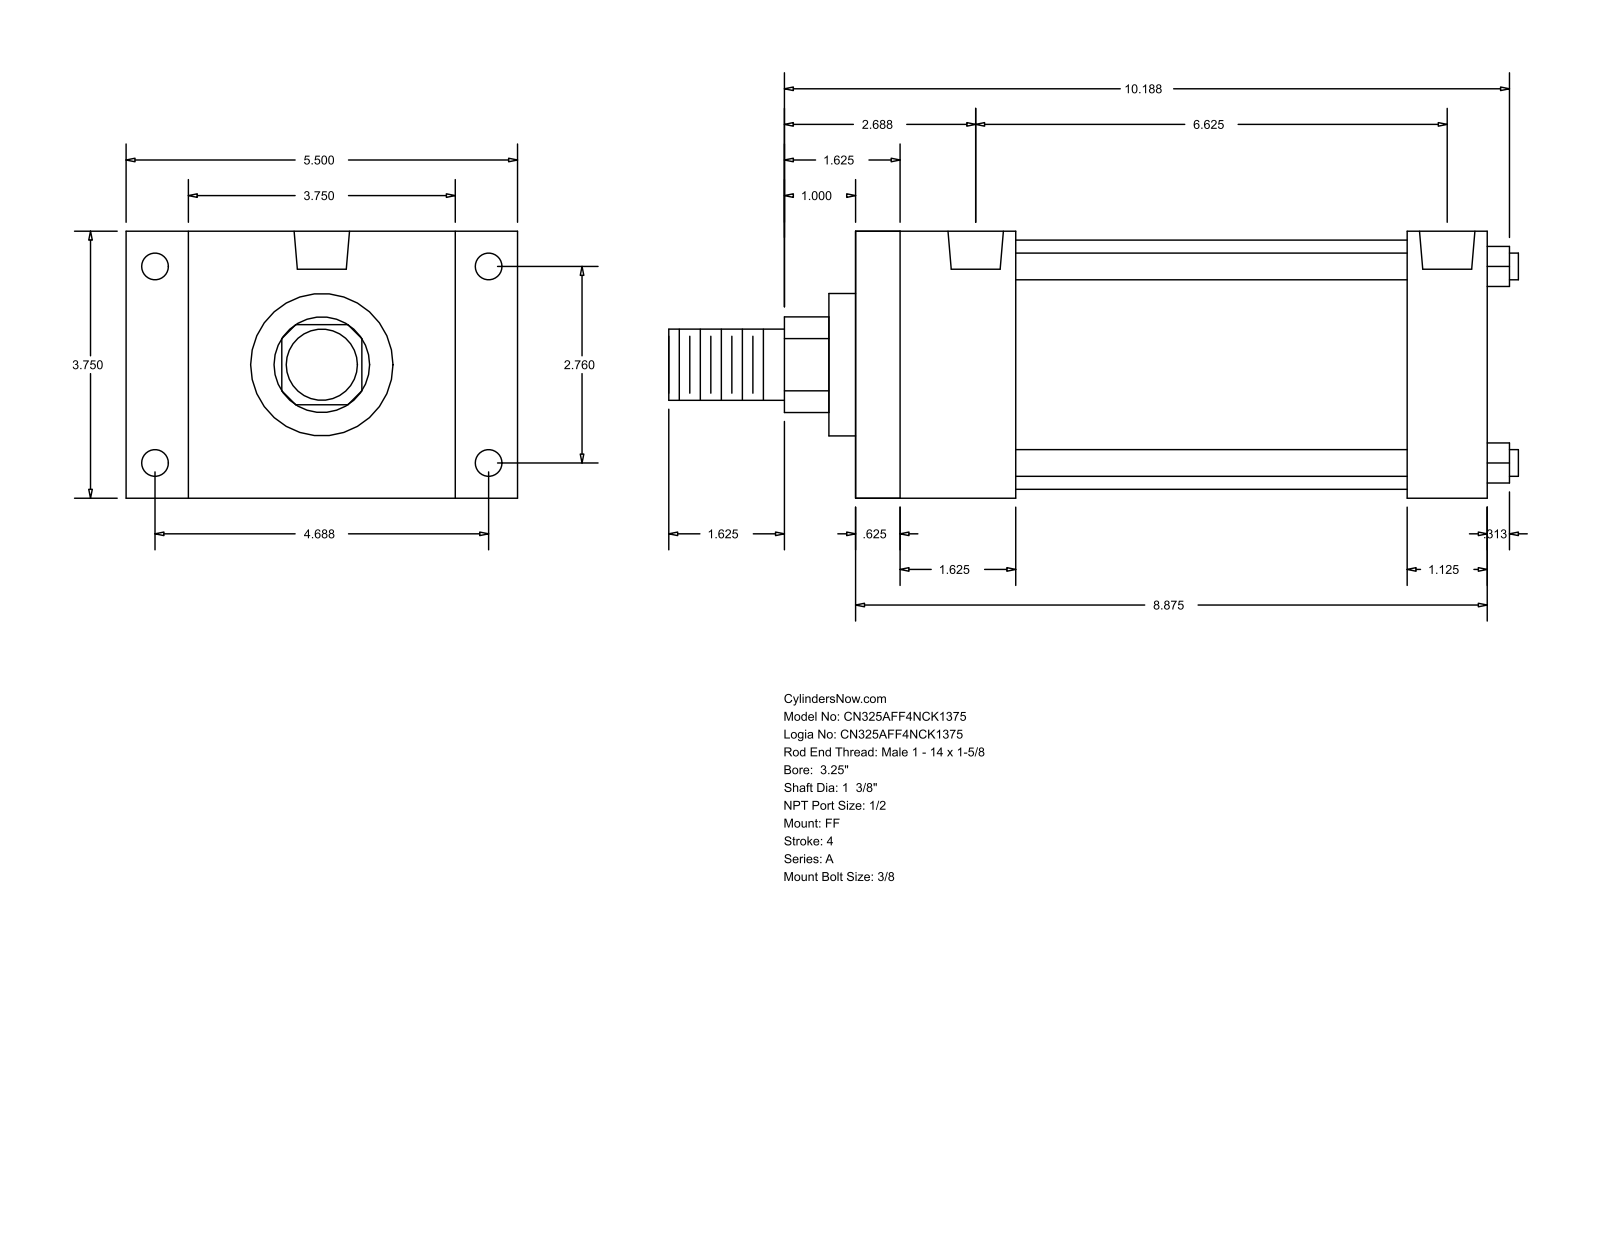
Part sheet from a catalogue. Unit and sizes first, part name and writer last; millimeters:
Units: millimetres
Overall size (bounding box): 303.21 × 139.7 × 95.25
Round holes (diameter × count): ⌀8.73 ×4, ⌀9.53 ×4, ⌀19.77 ×2
Round bosses / shafts (diameter × count): ⌀9.53 ×4, ⌀88.9 ×1, ⌀50.8 ×1, ⌀34.92 ×1, ⌀25.4 ×1
Partial cylindrical surfaces — rounded edges, fillets, slot ends (radius × count): R17.06 ×1
Main face-to-face distances: 95.24, 225.42, 209.55, 139.7, 15.87, 57.15, 22.23, 117.47, 28.57, 196.85
Hole centre spacings: 3.18, 70.1, 119.06, 138.16, 161.92, 165.1, 168.28
Bodies: 0 solids, 92 faces (64 planar, 28 cylindrical, 0 other)
Part name (STEP PRODUCT): A_FF__0325_1.375
STEP written by: GSSL Pune (CONFIG_CONTROL_DESIGN)
